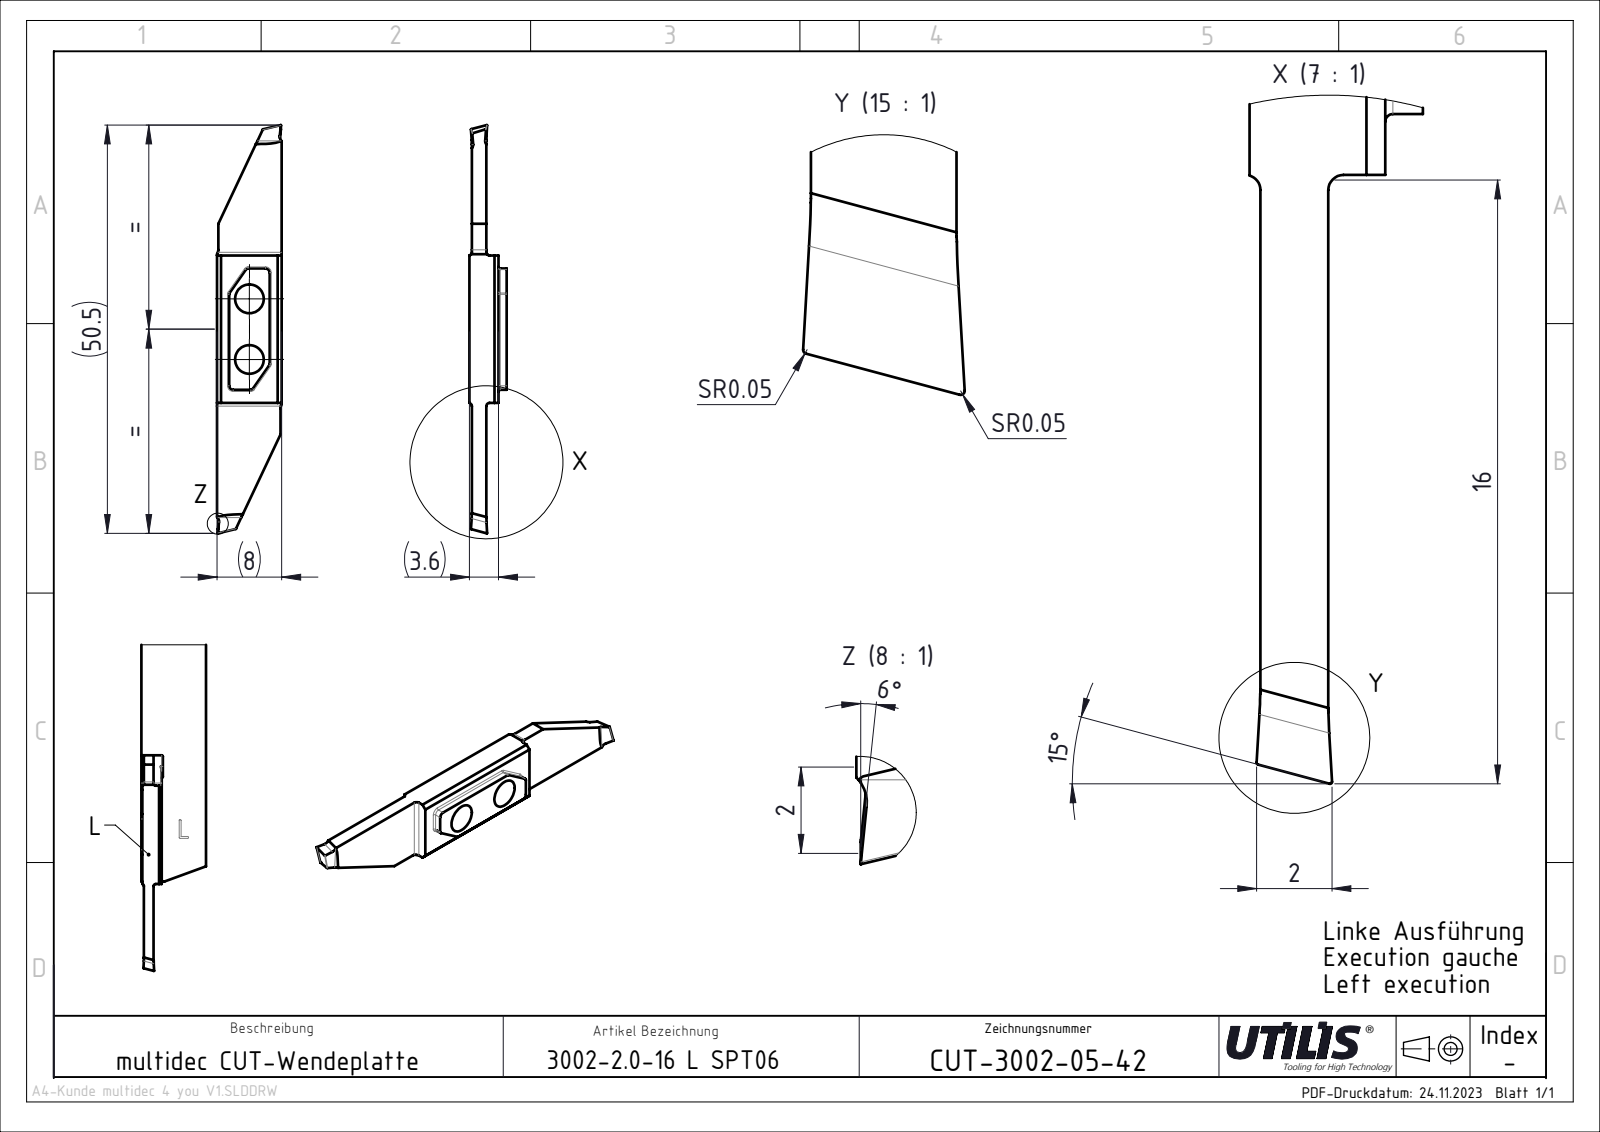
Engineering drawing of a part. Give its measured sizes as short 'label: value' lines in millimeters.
name: CUT-3002 SPT Slim_and_Deep; ASME Y14.5
written by: SolidWorks 2023 SP4 || FormatWorks Professional (AP242_MANAGED_MODEL_BASED_3D_ENGINEERING_MIM_LF)
unit: mm
bodies: 1 solid, 36 faces (22 planar, 14 cylindrical, 0 other)
size: 50.5 × 8 × 3.6
volume: 779 mm³; area: 968 mm²
holes: 2× ⌀3.55
rounds: 4× R0.4, 2× R1
face distances: 1.8, 2.09, 3.6, 3.31, 1.51, 8, 18.09, 7.85, 0.6, 18.22
hole spacings: 7.5
